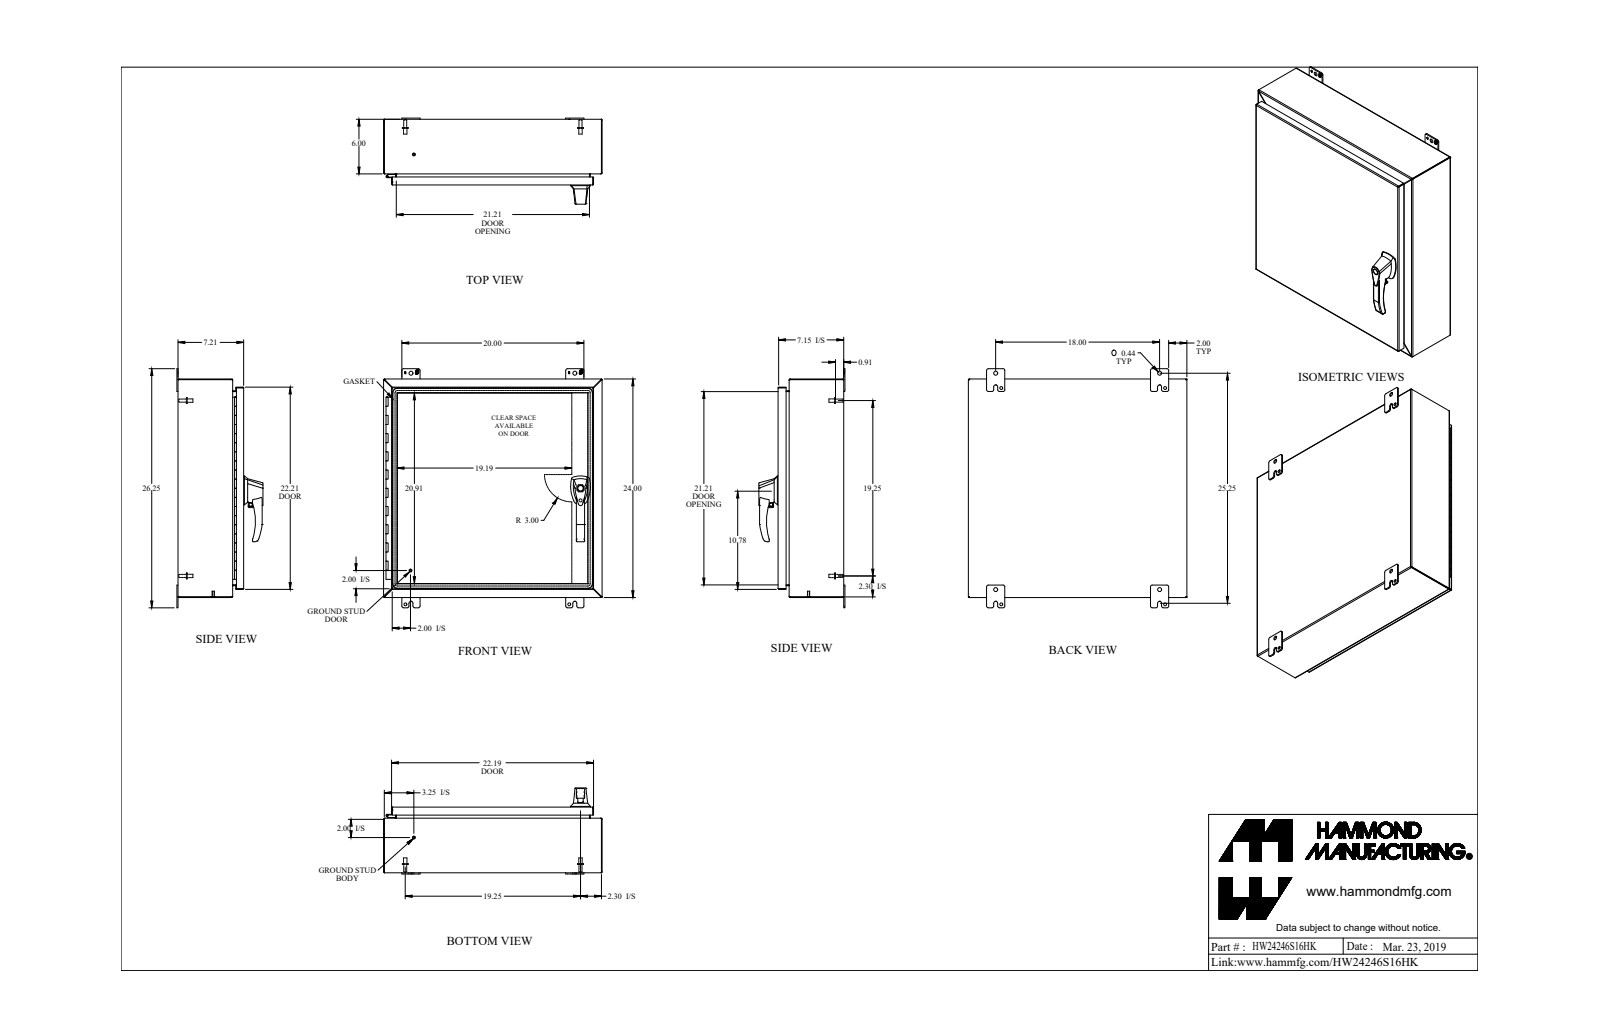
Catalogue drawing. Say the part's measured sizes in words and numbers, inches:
The part is named "HW24246S16HK". Its 3-D file was written by "SolidWorks 2018 (AUTOMOTIVE_DESIGN)". It is 42 solids with 1420 faces: 688 planar, 580 cylindrical and 152 other. Overall it measures 26.25 by 24 by 9.45 inches. Its volume is 172.3 cubic inches and its surface area 4 387 square inches. Round holes: 6 of diameter 0.176, 5 of diameter 0.313, 3 of diameter 0.25, 3 of diameter 0.265, 3 of diameter 0.413, 2 of diameter 0.196, 2 of diameter 0.256, 2 of diameter 0.394, 2 of diameter 0.437, 1 of diameter 0.11, 1 of diameter 0.233, 1 of diameter 0.33. Round bosses or shafts: 9 of diameter 0.375, 7 of diameter 0.25, 6 of diameter 0.156, 4 of diameter 0.65, 4 of diameter 0.332, 3 of diameter 1, 3 of diameter 0.51, 2 of diameter 0.63. Partial cylindrical surfaces (rounded edges, fillets, slot ends): 27 of radius 0.25, 24 of radius 0.188, 20 of radius 0.036, 20 of radius 0.108, 12 of radius 0.06, 9 of radius 0.125, 8 of radius 0.045, 8 of radius 0.218. The main face-to-face distances are 0.072, 0.072, 23.928, 7.138, 7.066, 7.138, 7.21, 23.856, 24, 5.928. The hole center spacings are 1.11, 8.118, 8.119, 16.237, 8.119, 18, 21.981, 1.004.
